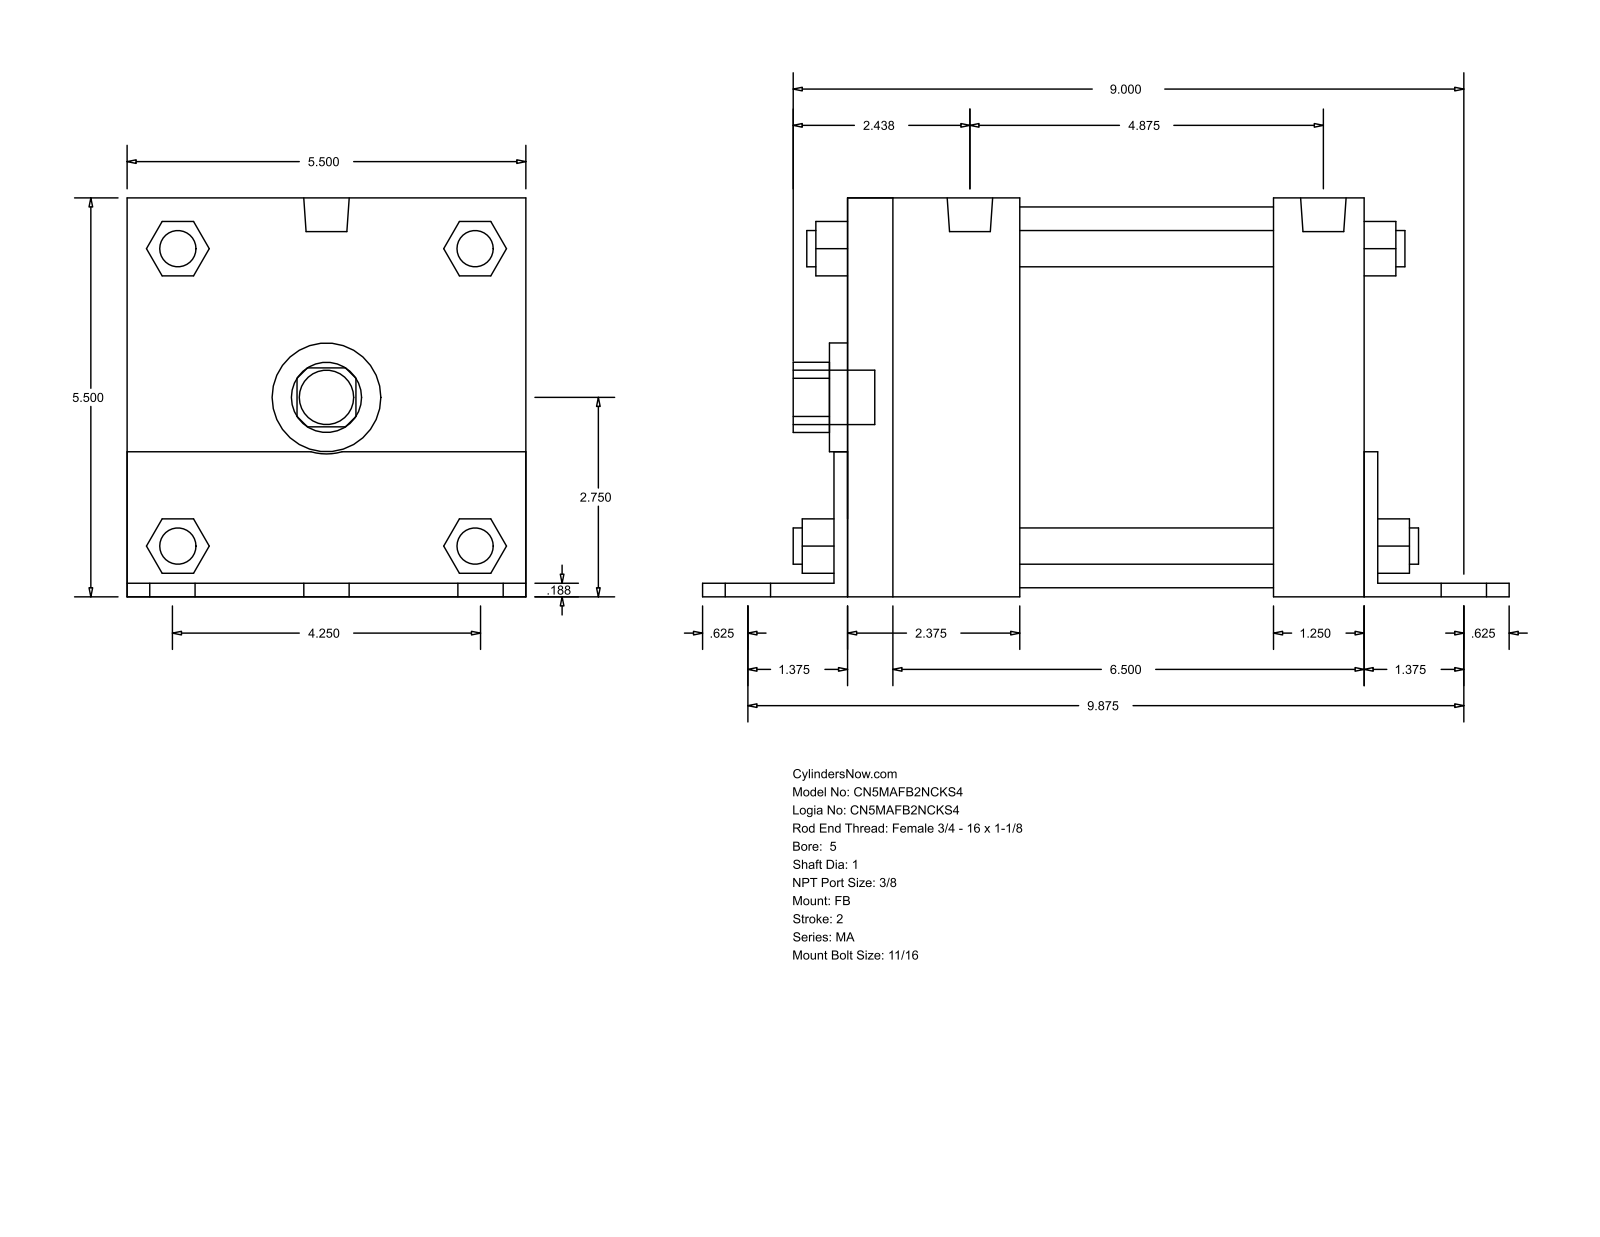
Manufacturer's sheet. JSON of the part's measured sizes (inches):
{"part_name": "MA_FB__0500_1", "step_written_by": "GSSL Pune (CONFIG_CONTROL_DESIGN)", "units": "inches", "bodies": {"solids": 0, "faces": 140, "planar": 105, "cylindrical": 35, "other": 0}, "overall_size": [11.125, 5.502, 5.5], "round_holes": [[1, 1], [1.5, 1], [5.25, 1]], "round_bosses_or_shafts": [[0.687, 6], [0.5, 4], [0.437, 4], [0.627, 2], [0.75, 1]], "partial_cylinders_radius": [[0.484, 1], [0.78, 1]], "face_to_face_distances": [5.5, 0.187, 5.502, 7.313, 0.185, 5.315, 7.125, 7.5, 1.25, 1.437]}
